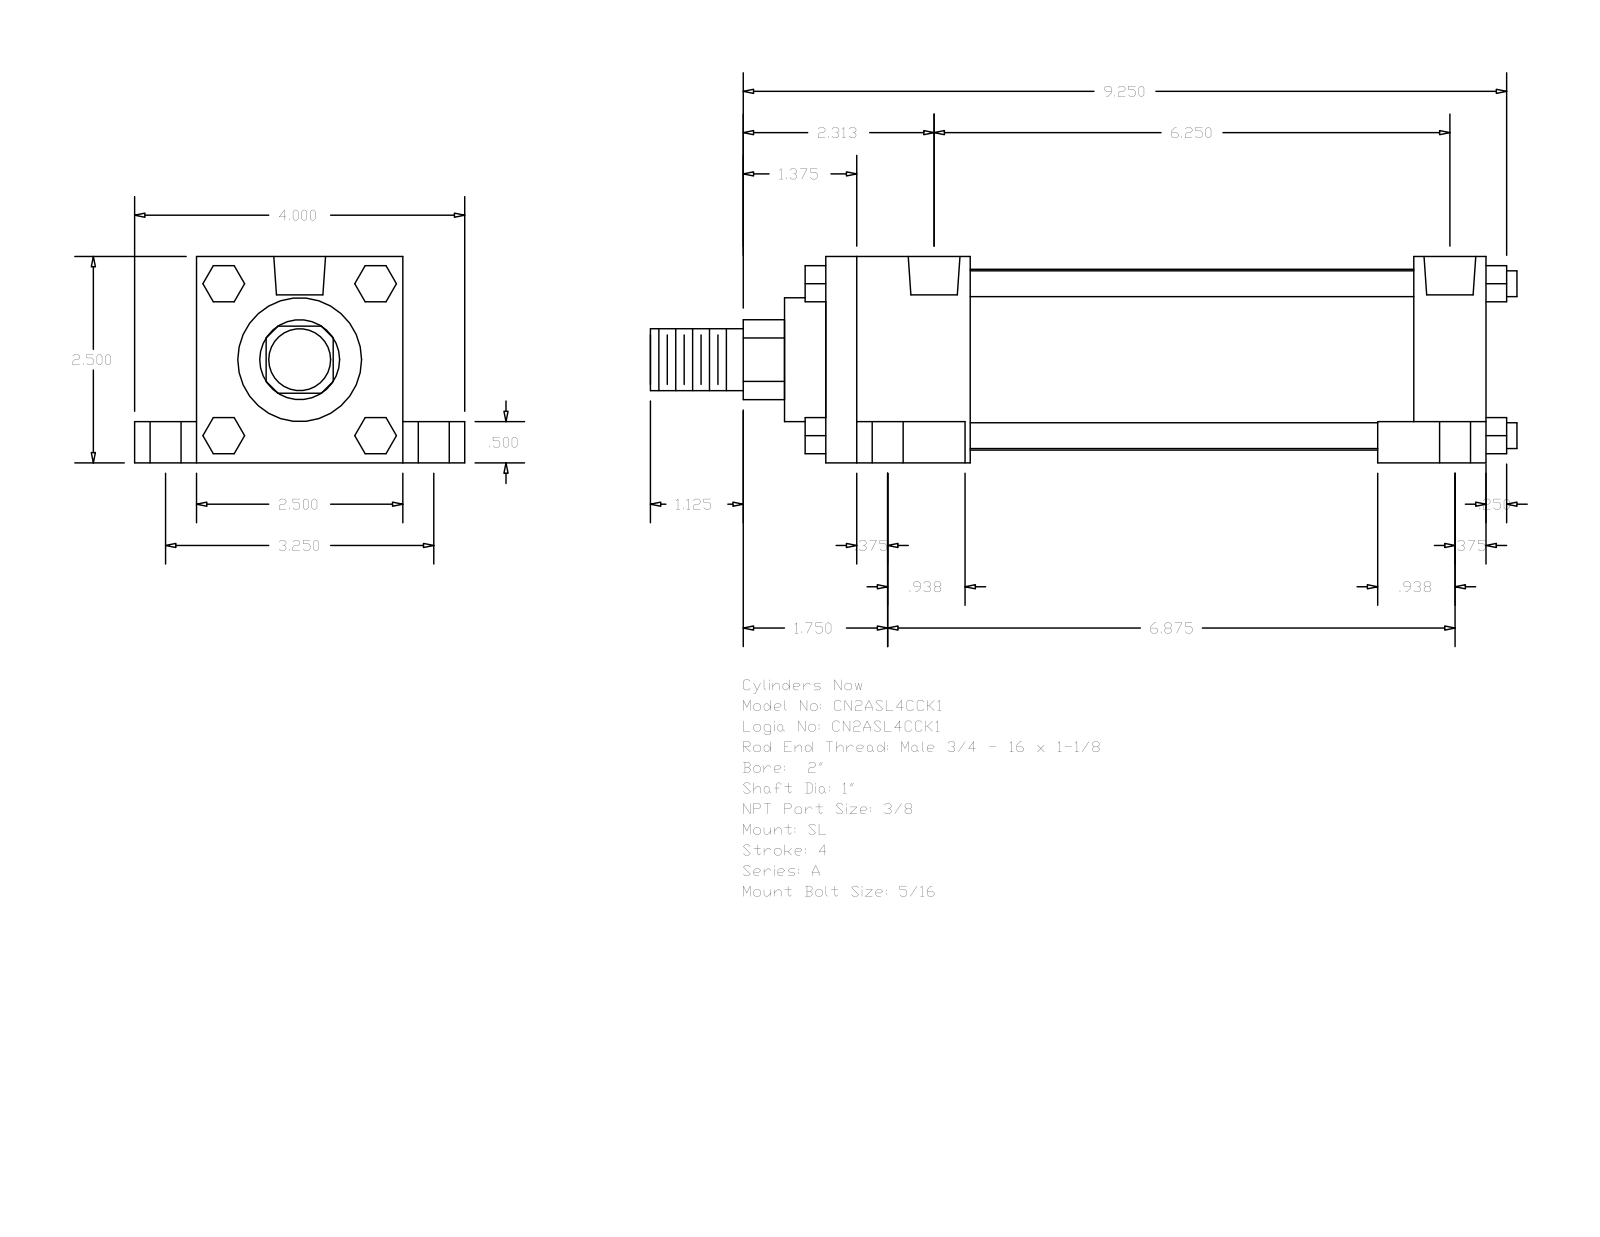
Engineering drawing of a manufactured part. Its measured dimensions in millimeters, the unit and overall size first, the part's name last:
Units: millimetres
Overall size (bounding box): 266.7 × 101.6 × 63.5
Round holes (diameter × count): ⌀5.56 ×4, ⌀9.53 ×4, ⌀15.88 ×4, ⌀15.93 ×2
Round bosses / shafts (diameter × count): ⌀7.94 ×4, ⌀55.63 ×1, ⌀38.1 ×1, ⌀25.4 ×1, ⌀19.05 ×1
Partial cylindrical surfaces — rounded edges, fillets, slot ends (radius × count): R12.29 ×1
Main face-to-face distances: 63.5, 203.2, 12.7, 50.8, 22.22, 19.05, 82.55, 44.45, 158.75, 180.98
Hole centre spacings: 41.3, 41.64, 43.67, 44.22, 82.54, 153.18, 164.02, 165.56
Bodies: 0 solids, 148 faces (112 planar, 36 cylindrical, 0 other)
Part name (STEP PRODUCT): A_SL__0200_1
STEP written by: GSSL Pune (CONFIG_CONTROL_DESIGN)
